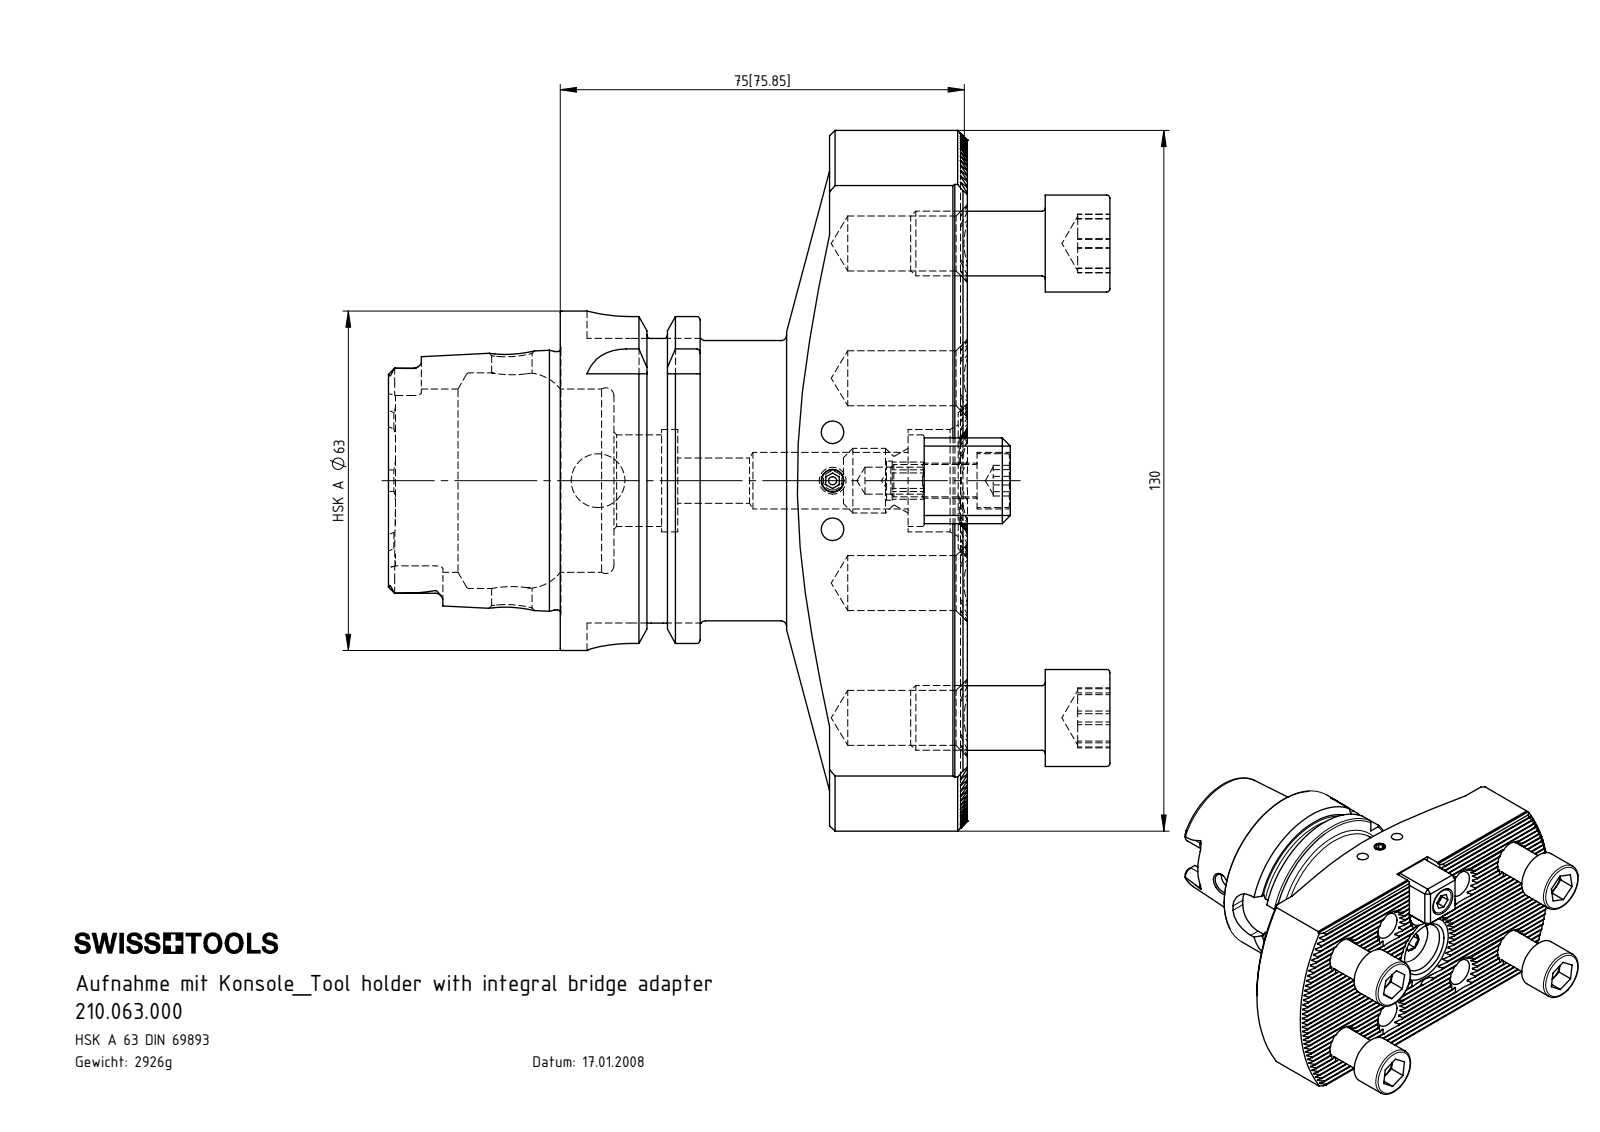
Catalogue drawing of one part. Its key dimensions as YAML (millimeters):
part_name: "ISO 4762 M12 x 25; Ko1-ER1.001.016_A; DIN 908 - M12x1.5; ISO 4026 - M5 x 8_ISO 4026 - M5 x 8 (+3 more)"
step_written_by: "SolidWorks 2017 (CONFIG_CONTROL_DESIGN)"
units: millimeters
bodies: {solids: 10, faces: 945, planar: 517, cylindrical: 226, other: 202}
overall_size: [133.93, 130, 70]
volume: 372684
surface_area: 74529
round_holes:
  - {diameter: 10.2, count: 8}
  - {diameter: 4.2, count: 3}
  - {diameter: 10.5, count: 2}
  - {diameter: 1.5, count: 1}
  - {diameter: 5, count: 1}
  - {diameter: 6.5, count: 1}
  - {diameter: 7.24, count: 1}
  - {diameter: 7.5, count: 1}
  - {diameter: 8.4, count: 1}
  - {diameter: 10, count: 1}
  - {diameter: 17, count: 1}
  - {diameter: 19, count: 1}
round_bosses_or_shafts:
  - {diameter: 12, count: 5}
  - {diameter: 18, count: 4}
  - {diameter: 63, count: 1}
  - {diameter: 54.95, count: 1}
  - {diameter: 52, count: 1}
  - {diameter: 47.94, count: 1}
  - {diameter: 10, count: 1}
  - {diameter: 6, count: 1}
partial_cylinders:
  - {radius: 0.14, count: 34}
  - {radius: 1.4, count: 6}
  - {radius: 2.88, count: 4}
  - {radius: 8, count: 4}
  - {radius: 7.95, count: 1}
  - {radius: 65, count: 1}
face_to_face_distances: [1.73, 17.32, 70, 8.66, 3.46, 5.2, 6.93, 15.59, 19.05, 3.47]
hole_center_spacings: [25, 27.59, 40, 47.17, 48.33, 63, 74.63, 9]
